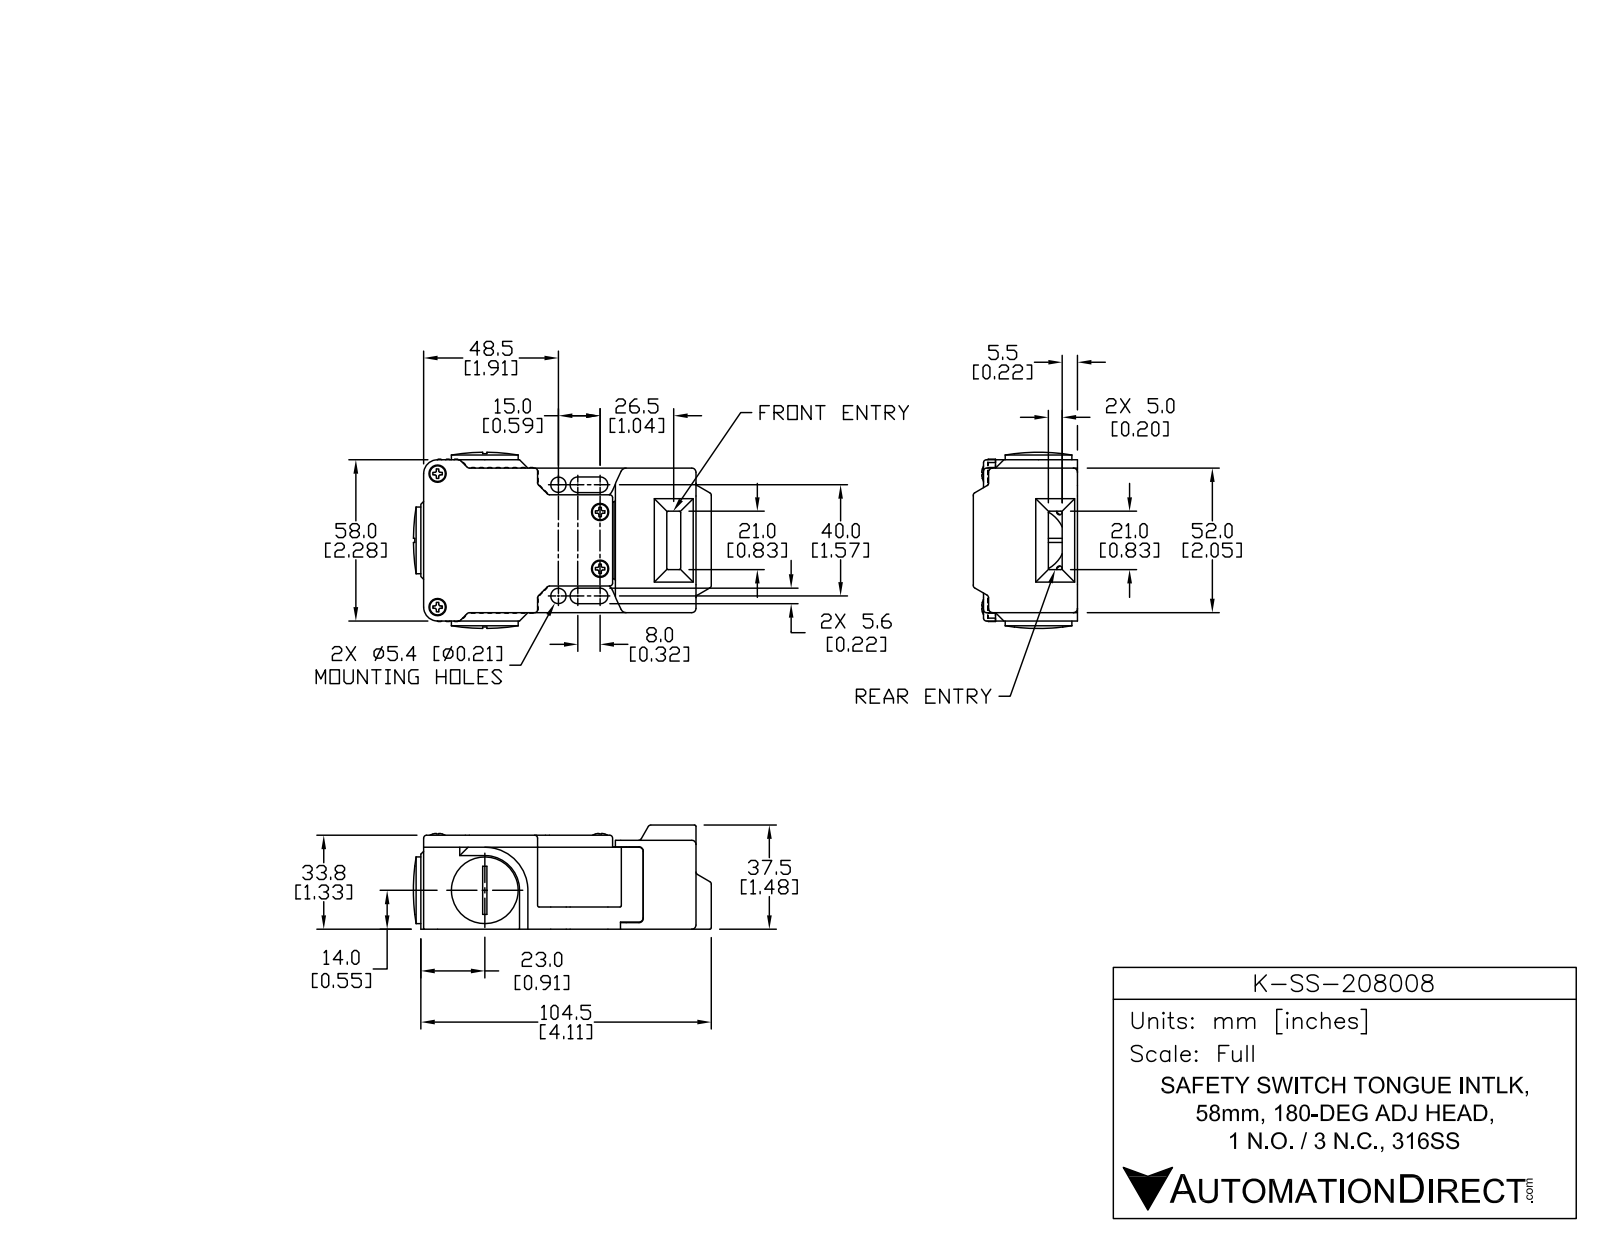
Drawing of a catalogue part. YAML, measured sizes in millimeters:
part_name: "K-SS-208008"
step_written_by: "SolidWorks 2013 (AUTOMOTIVE_DESIGN)"
units: millimeters
bodies: {solids: 1, faces: 235, planar: 164, cylindrical: 44, other: 27}
overall_size: [100.75, 60.2, 38]
volume: 159050
surface_area: 27548
round_holes:
  - {diameter: 5.4, count: 2}
  - {diameter: 19.33, count: 1}
  - {diameter: 20, count: 1}
round_bosses_or_shafts:
  - {diameter: 5.6, count: 2}
  - {diameter: 23.8, count: 1}
partial_cylinders:
  - {radius: 1.5, count: 12}
  - {radius: 2, count: 4}
  - {radius: 2.75, count: 4}
  - {radius: 4, count: 3}
  - {radius: 5, count: 2}
face_to_face_distances: [3, 55, 33.5, 52, 96, 33.45, 58, 1.05, 5, 4.1]
hole_center_spacings: [40]
